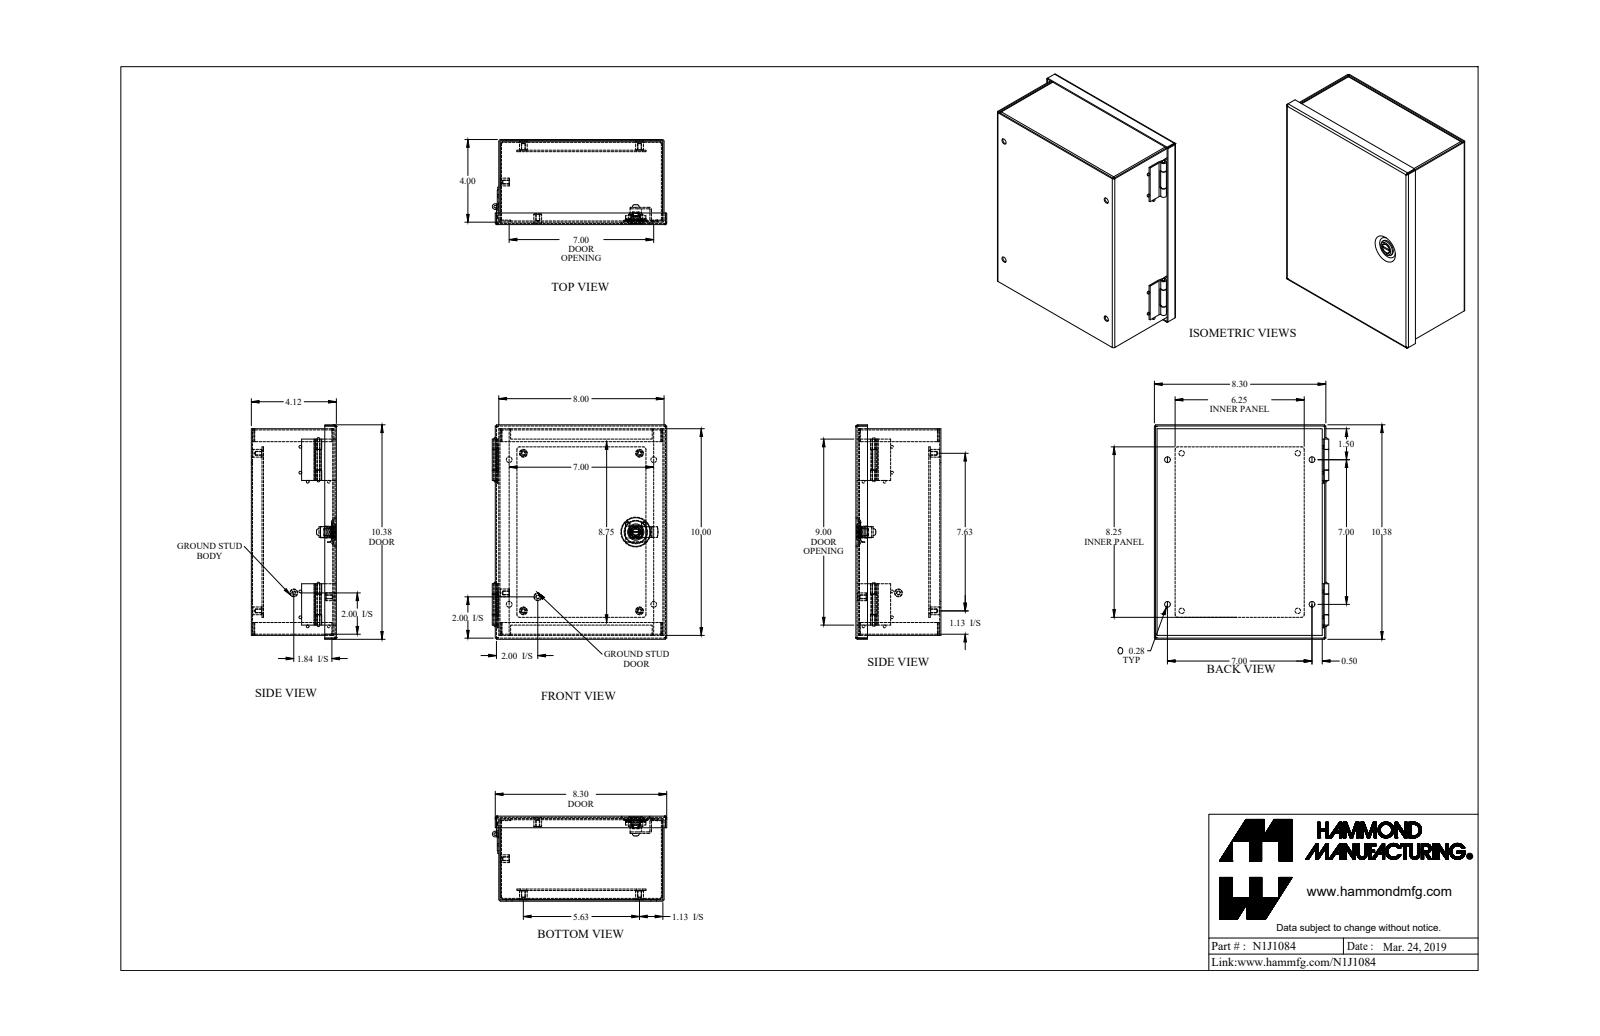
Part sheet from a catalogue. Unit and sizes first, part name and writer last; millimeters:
Units: millimetres
Overall size (bounding box): 263.7 × 214.5 × 104.6
Round holes (diameter × count): ⌀4 ×6, ⌀6.7 ×4, ⌀7.1 ×4, ⌀3.2 ×1, ⌀8.1 ×1, ⌀12.1 ×1
Round bosses / shafts (diameter × count): ⌀3.3 ×8, ⌀9.5 ×6, ⌀20 ×1, ⌀13.9 ×1, ⌀12 ×1, ⌀11.9 ×1, ⌀9.3 ×1, ⌀8.1 ×1
Partial cylindrical surfaces — rounded edges, fillets, slot ends (radius × count): R0.7 ×16, R2.2 ×16, R0.3 ×4, R2.5 ×4, R3.2 ×4, R0.9 ×2, R2 ×2, R6.4 ×2
Main face-to-face distances: 1.4, 103.1, 101.7, 104.6, 201.8, 252.6, 1.8, 13.1, 11.7, 90
Hole centre spacings: 19.2, 160.5, 177.8, 186.6, 245.4, 91.6, 97, 142.9
Volume: 411 000 mm³ · Surface area: 551 200 mm²
Bodies: 18 solids, 477 faces (224 planar, 188 cylindrical, 65 other)
Part name (STEP PRODUCT): N1J1084
STEP written by: SolidWorks 2018 (AUTOMOTIVE_DESIGN)
